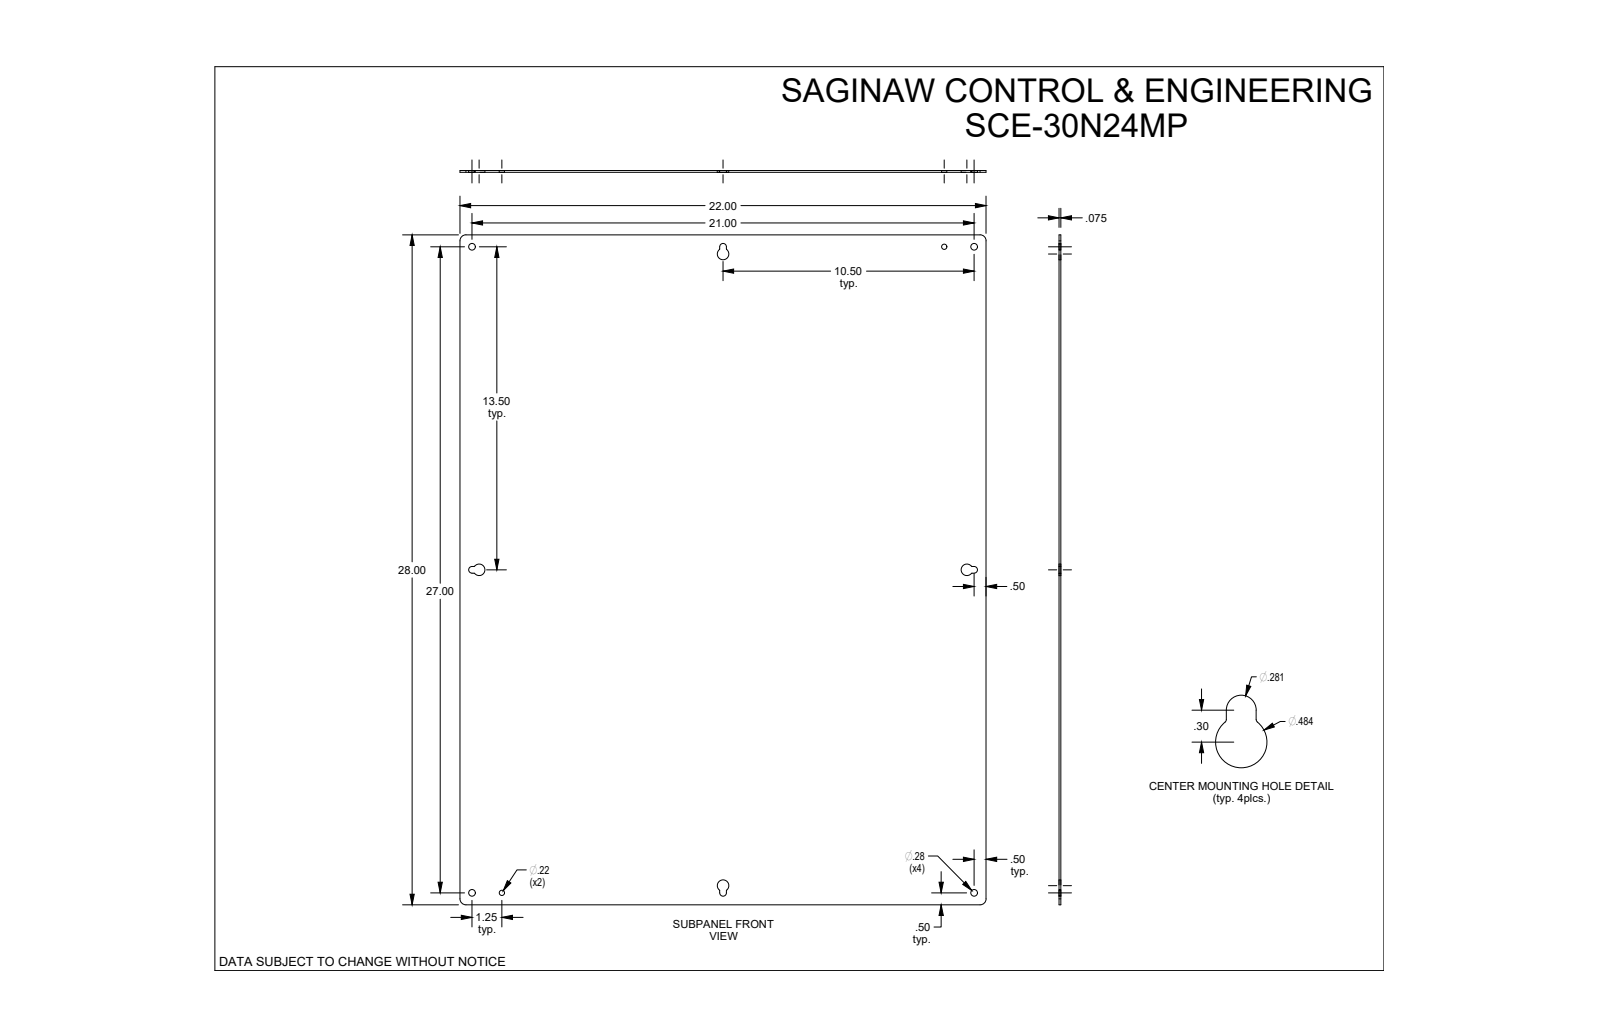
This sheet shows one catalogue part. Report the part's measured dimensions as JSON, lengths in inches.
{"part_name": "SCE-30N24MP", "step_written_by": "SolidWorks 2019 (CONFIG_CONTROL_DESIGN)", "units": "inches", "bodies": {"solids": 1, "faces": 40, "planar": 14, "cylindrical": 26, "other": 0}, "overall_size": [28, 22, 0.075], "volume_in3": 46.1, "surface_area_in2": 1238, "round_holes": [[0.281, 4], [0.218, 2]], "partial_cylinders_radius": [[0.03, 8], [0.141, 4], [0.242, 4], [0.25, 4]], "face_to_face_distances": [0.075, 22, 28, 13.859, 14.141, 0.281, 10.859, 11.141], "hole_center_spacings": [1.25, 19.75, 21, 27, 27.029, 33.452, 34.205, 32.73]}
